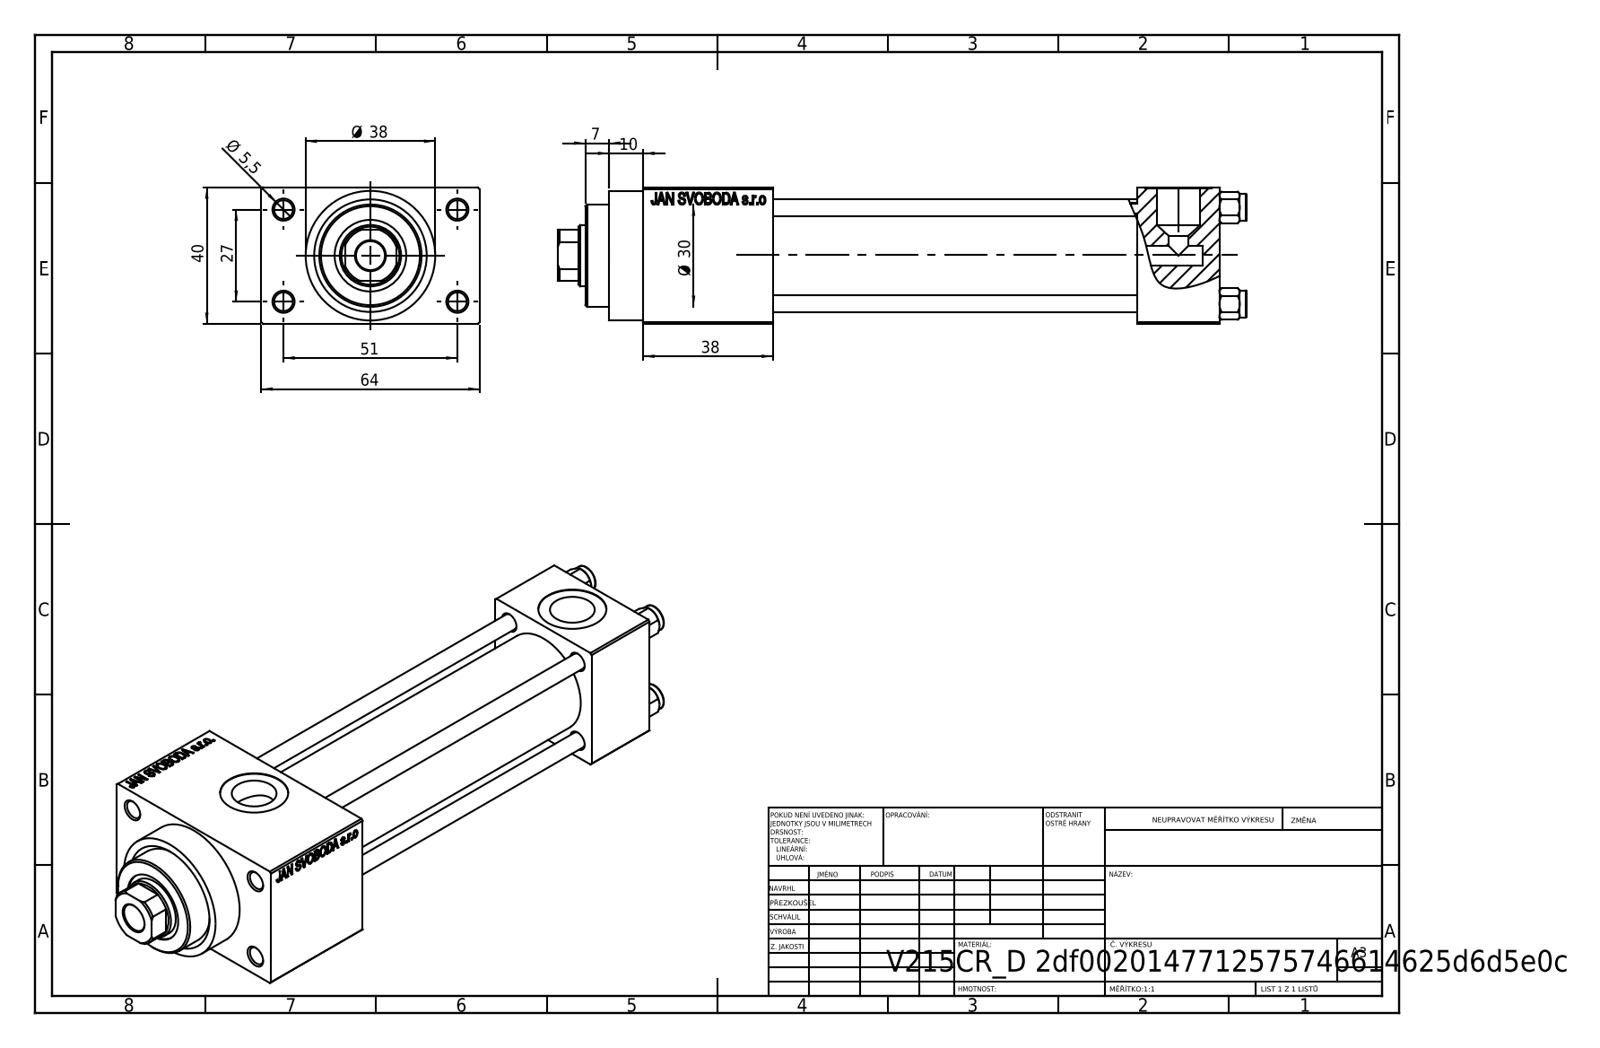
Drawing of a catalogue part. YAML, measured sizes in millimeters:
part_name: "V215_VC_A; V215CR_VCP_D; V215CR_D_TYCINKA; V215CR_D_Body (+1 more)"
step_written_by: "SolidWorks 2019 (CONFIG_CONTROL_DESIGN)"
units: millimeters
bodies: {solids: 11, faces: 1102, planar: 495, cylindrical: 87, other: 520}
overall_size: [202, 64, 40]
volume: 216488
surface_area: 81853
round_holes:
  - {diameter: 5, count: 4}
  - {diameter: 5.5, count: 4}
  - {diameter: 20, count: 3}
  - {diameter: 7, count: 2}
  - {diameter: 13.16, count: 2}
  - {diameter: 8.5, count: 1}
  - {diameter: 18, count: 1}
  - {diameter: 21, count: 1}
  - {diameter: 25, count: 1}
  - {diameter: 30, count: 1}
round_bosses_or_shafts:
  - {diameter: 8, count: 4}
  - {diameter: 38, count: 1}
  - {diameter: 31, count: 1}
partial_cylinders:
  - {radius: 8.5, count: 1}
face_to_face_distances: [40, 12, 52, 107, 24, 131, 64, 38, 169, 145]
hole_center_spacings: [11.37, 20.01, 28.3, 28.85, 29.89, 39.66, 48.34, 27]
